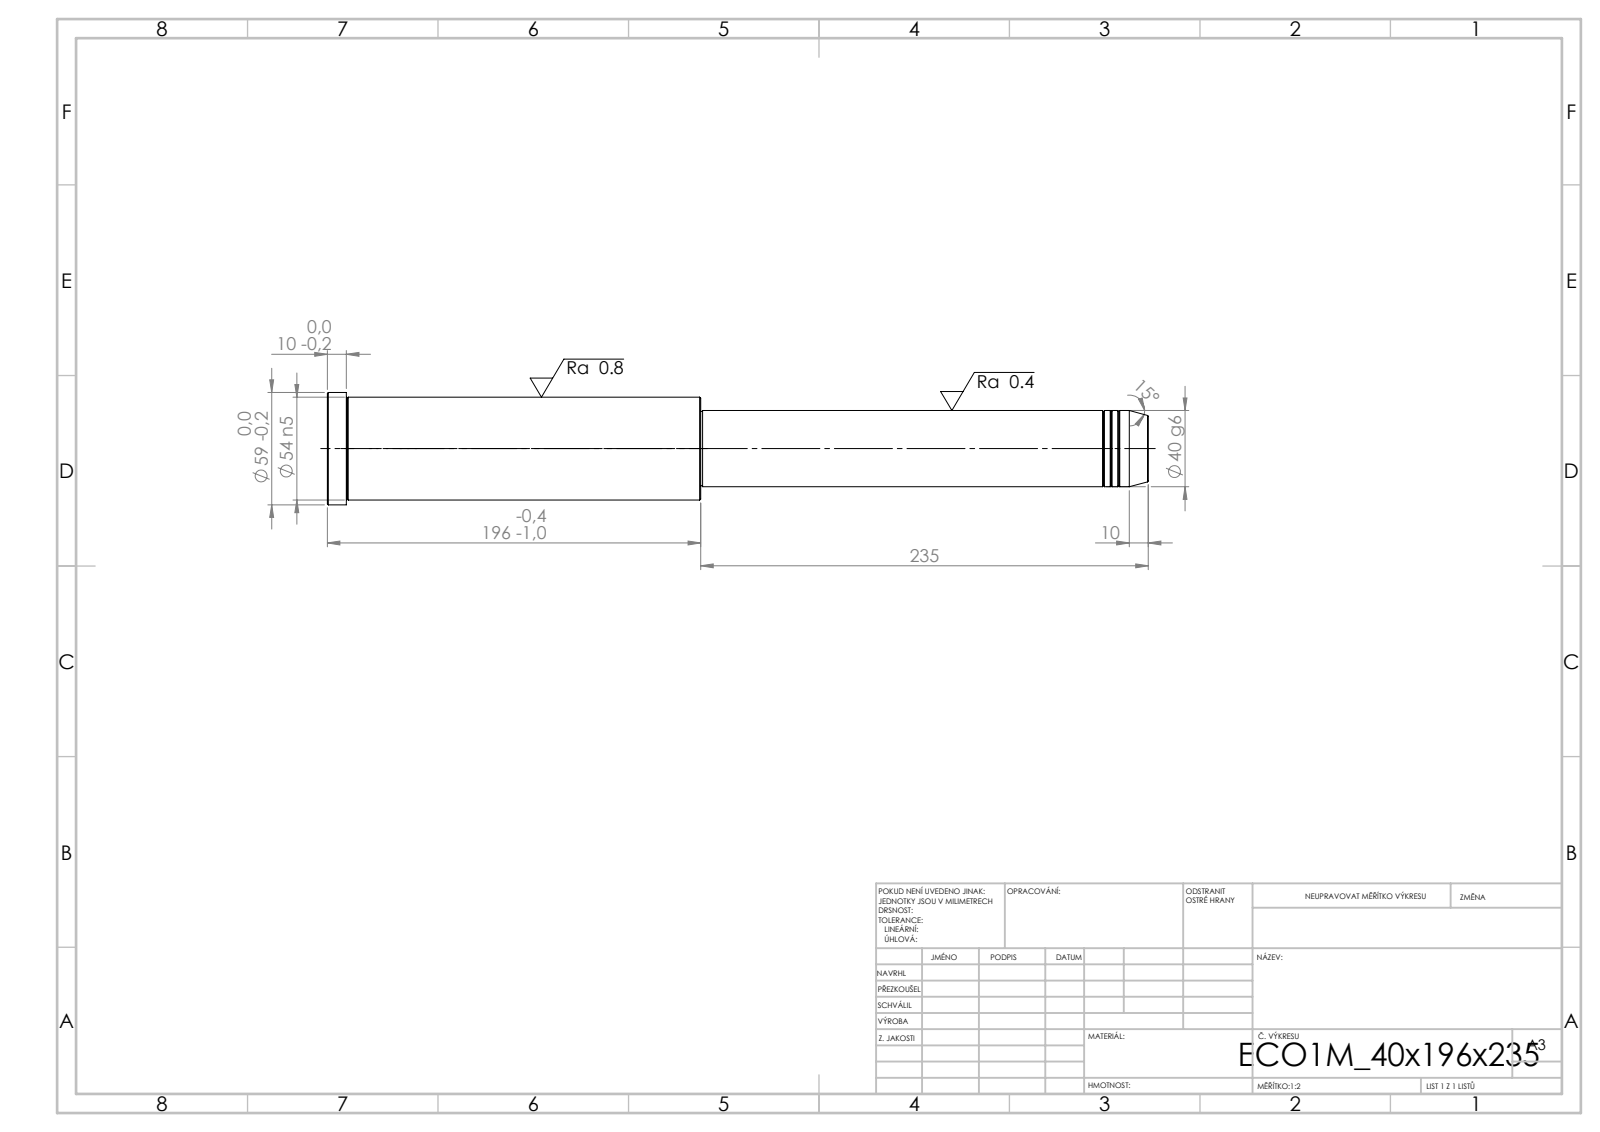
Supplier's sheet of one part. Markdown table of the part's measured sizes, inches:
| quantity | value |
| --- | --- |
| STEP written by | SolidWorks 2019 (CONFIG_CONTROL_DESIGN) |
| units | inches |
| bodies | 1 solid, 43 faces (5 planar, 14 cylindrical, 24 other) |
| overall size | 16.969 × 2.323 × 2.323 |
| volume | 45.57 in³ |
| surface area | 105.9 in² |
| round bosses / shafts (diameter × count) | 2.323 × 1, 2.126 × 1, 1.575 × 1, 1.535 × 1 |
| main face-to-face distances | 7.717, 9.252, 16.969, 16.575, 7.323, 0.394, 9.213, 0.039, 7.362, 7.756 |
